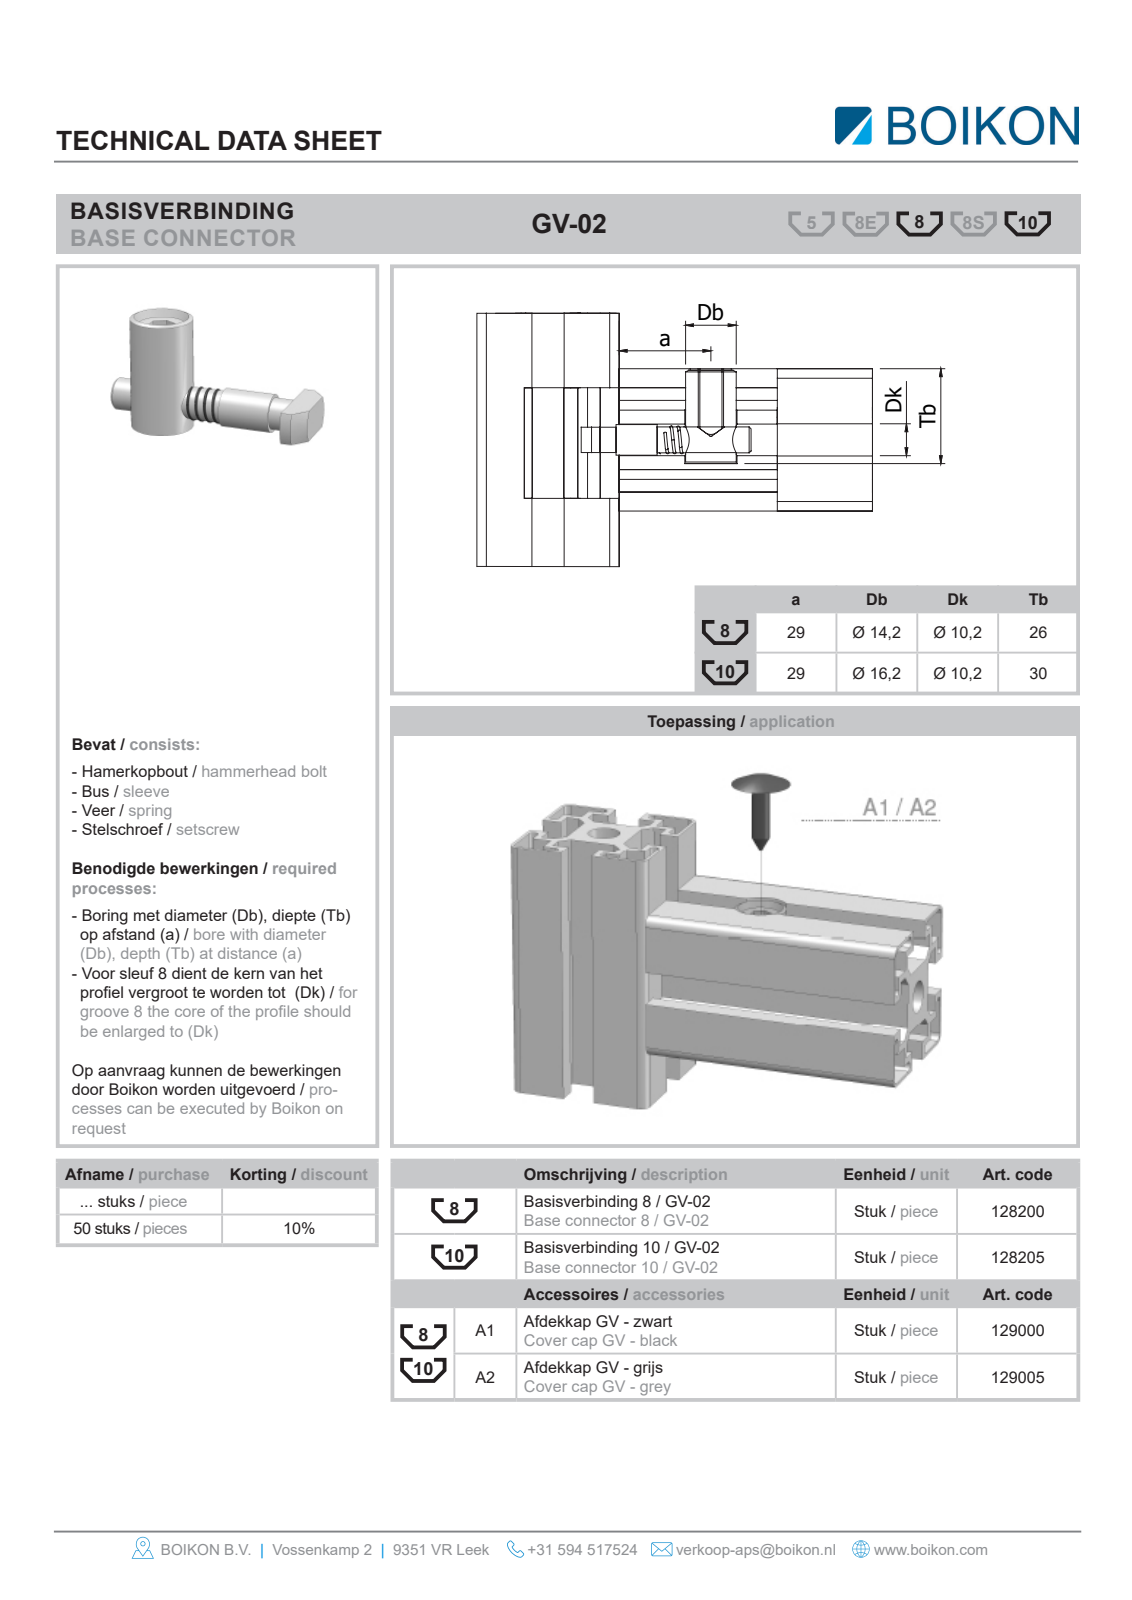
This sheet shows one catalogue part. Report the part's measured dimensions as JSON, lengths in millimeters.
{"part_name": "Root; 128200Basisverbinding 8 / GV-02BOIKON", "step_written_by": "HiCAD 2013 1802.4 Build 509 (AUTOMOTIVE_DESIGN)", "units": "millimeters", "bodies": {"solids": 1, "faces": 27, "planar": 17, "cylindrical": 7, "other": 3}, "overall_size": [51.7, 24, 17], "volume_mm3": 6111, "surface_area_mm2": 2783, "round_bosses_or_shafts": [[14, 1], [9.8, 1], [8.3, 1]], "partial_cylinders_radius": [[8.5, 1]], "face_to_face_distances": [24, 6, 5, 1.7, 22.3, 10, 8.3, 14, 36.2, 42.2]}
